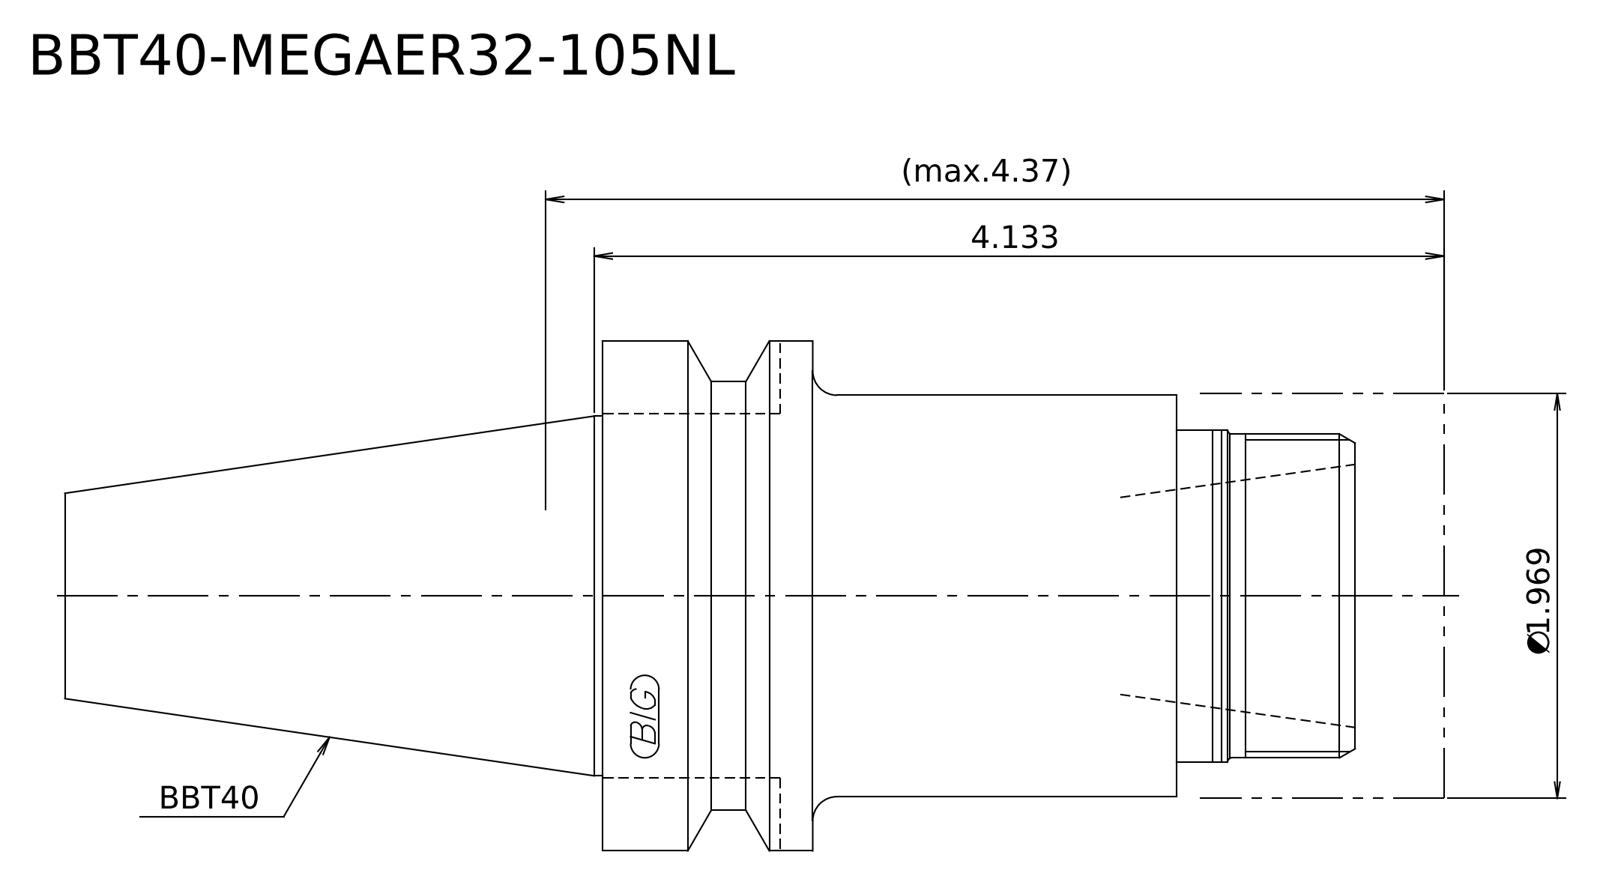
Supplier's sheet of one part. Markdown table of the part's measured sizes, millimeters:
| quantity | value |
| --- | --- |
| STEP written by | Kubotek KeyCreator 2011 V10.0.2 (22737) (automotive_design) |
| units | millimeters |
| bodies | 2 solids, 21 faces (6 planar, 8 cylindrical, 7 other) |
| overall size | 170.4 × 63 × 63 |
| volume | 315 044 mm³ |
| surface area | 36 623 mm² |
| round bosses / shafts (diameter × count) | 63 × 1, 53 × 1, 50 × 1, 49.6 × 1, 44.45 × 1, 41 × 1, 40 × 1 |
| main face-to-face distances | 30.2, 104, 73.8, 11, 19.2, 93, 33, 22, 2.8, 71 |
